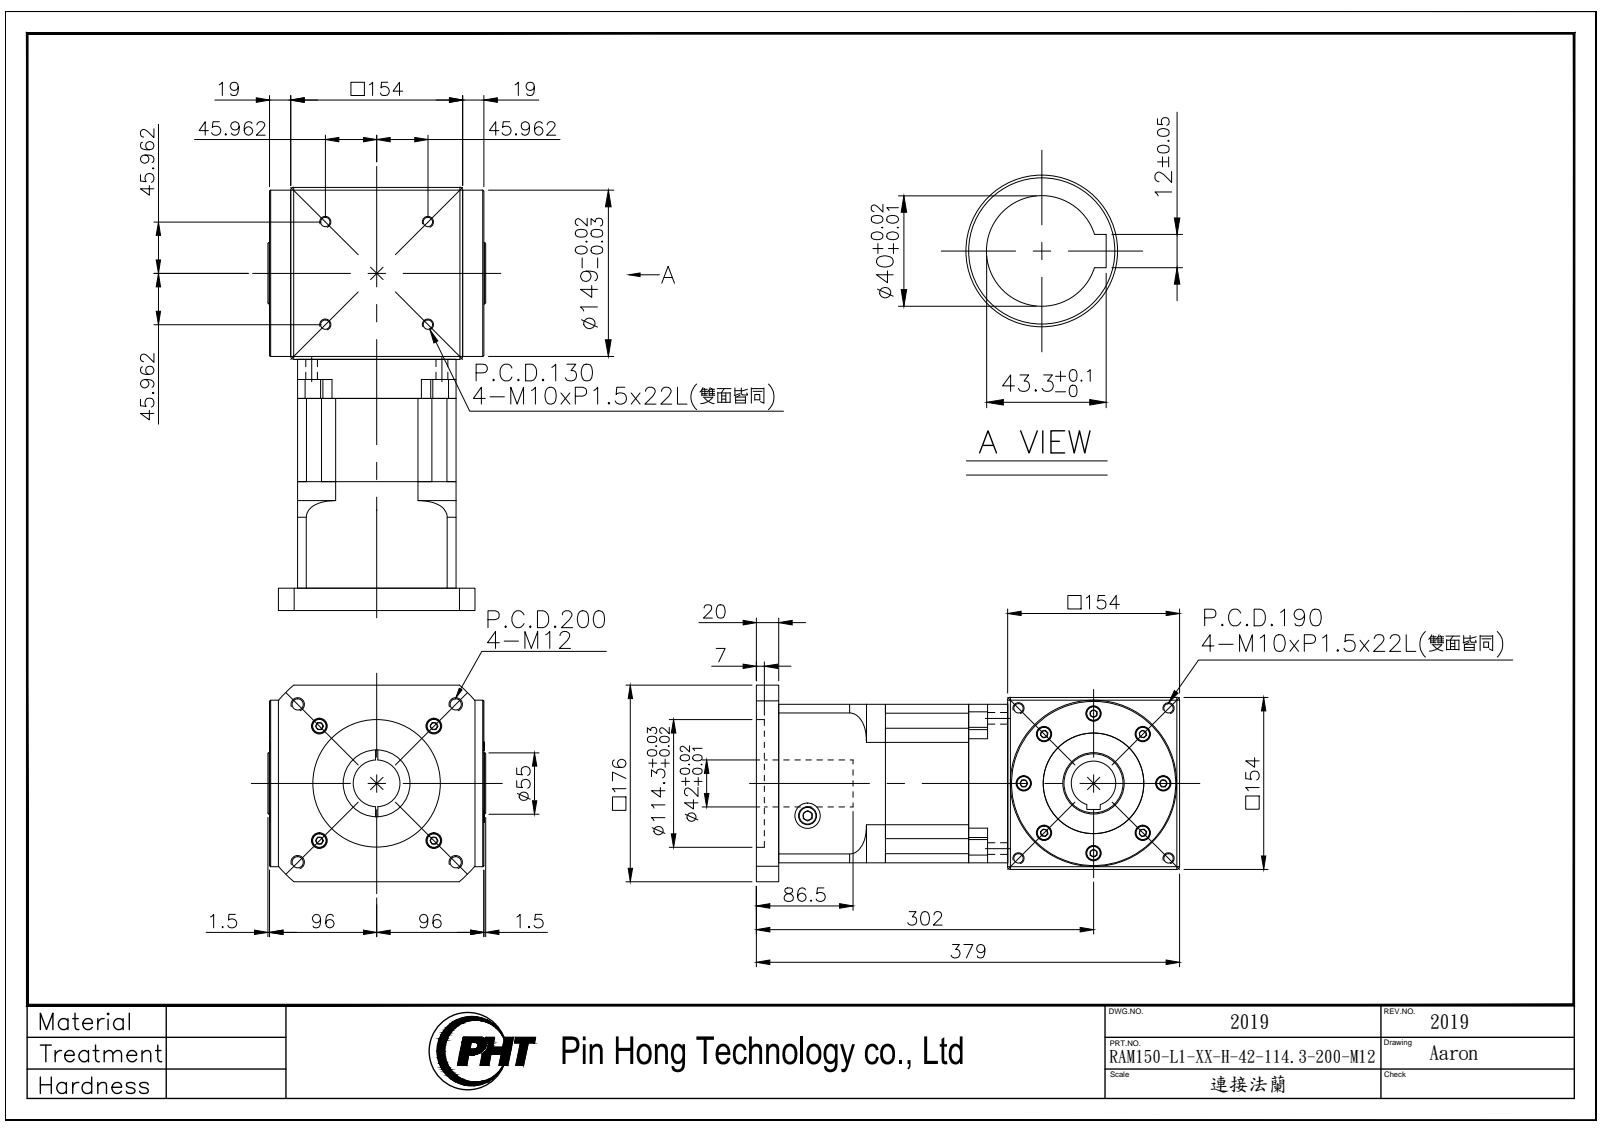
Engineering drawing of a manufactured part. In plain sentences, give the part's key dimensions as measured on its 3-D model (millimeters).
The part is named "RAM150-L2-XX-H-42-114.3-200-M12_2019". Its 3-D file was written by "SolidWorks 2016 (AUTOMOTIVE_DESIGN)". It is 4 solids with 875 faces: 415 planar, 312 cylindrical and 148 other. Overall it measures 379 by 195 by 176 millimeters. Its volume is 8 032 000 cubic millimeters and its surface area 588 700 square millimeters. Round holes: 12 of diameter 8.5, 12 of diameter 9, 12 of diameter 14, 8 of diameter 11, 8 of diameter 17.5, 4 of diameter 6.8, 4 of diameter 10.2, 4 of diameter 10.5, 2 of diameter 22.5, 1 of diameter 40, 1 of diameter 40.6, 1 of diameter 42. Round bosses or shafts: 12 of diameter 16, 4 of diameter 13, 1 of diameter 149, 1 of diameter 130, 1 of diameter 90, 1 of diameter 74, 1 of diameter 55. Partial cylindrical surfaces (rounded edges, fillets, slot ends): 4 of radius 10, 1 of radius 80, 1 of radius 95, 1 of radius 107.4, 1 of radius 115. The main face-to-face distances are 6, 148, 154, 142, 74.5, 109.5, 35, 25, 263.5, 189. The hole center spacings are 71, 18.72, 18.79, 23.06, 36.4, 47.83, 67.34, 82.93.
